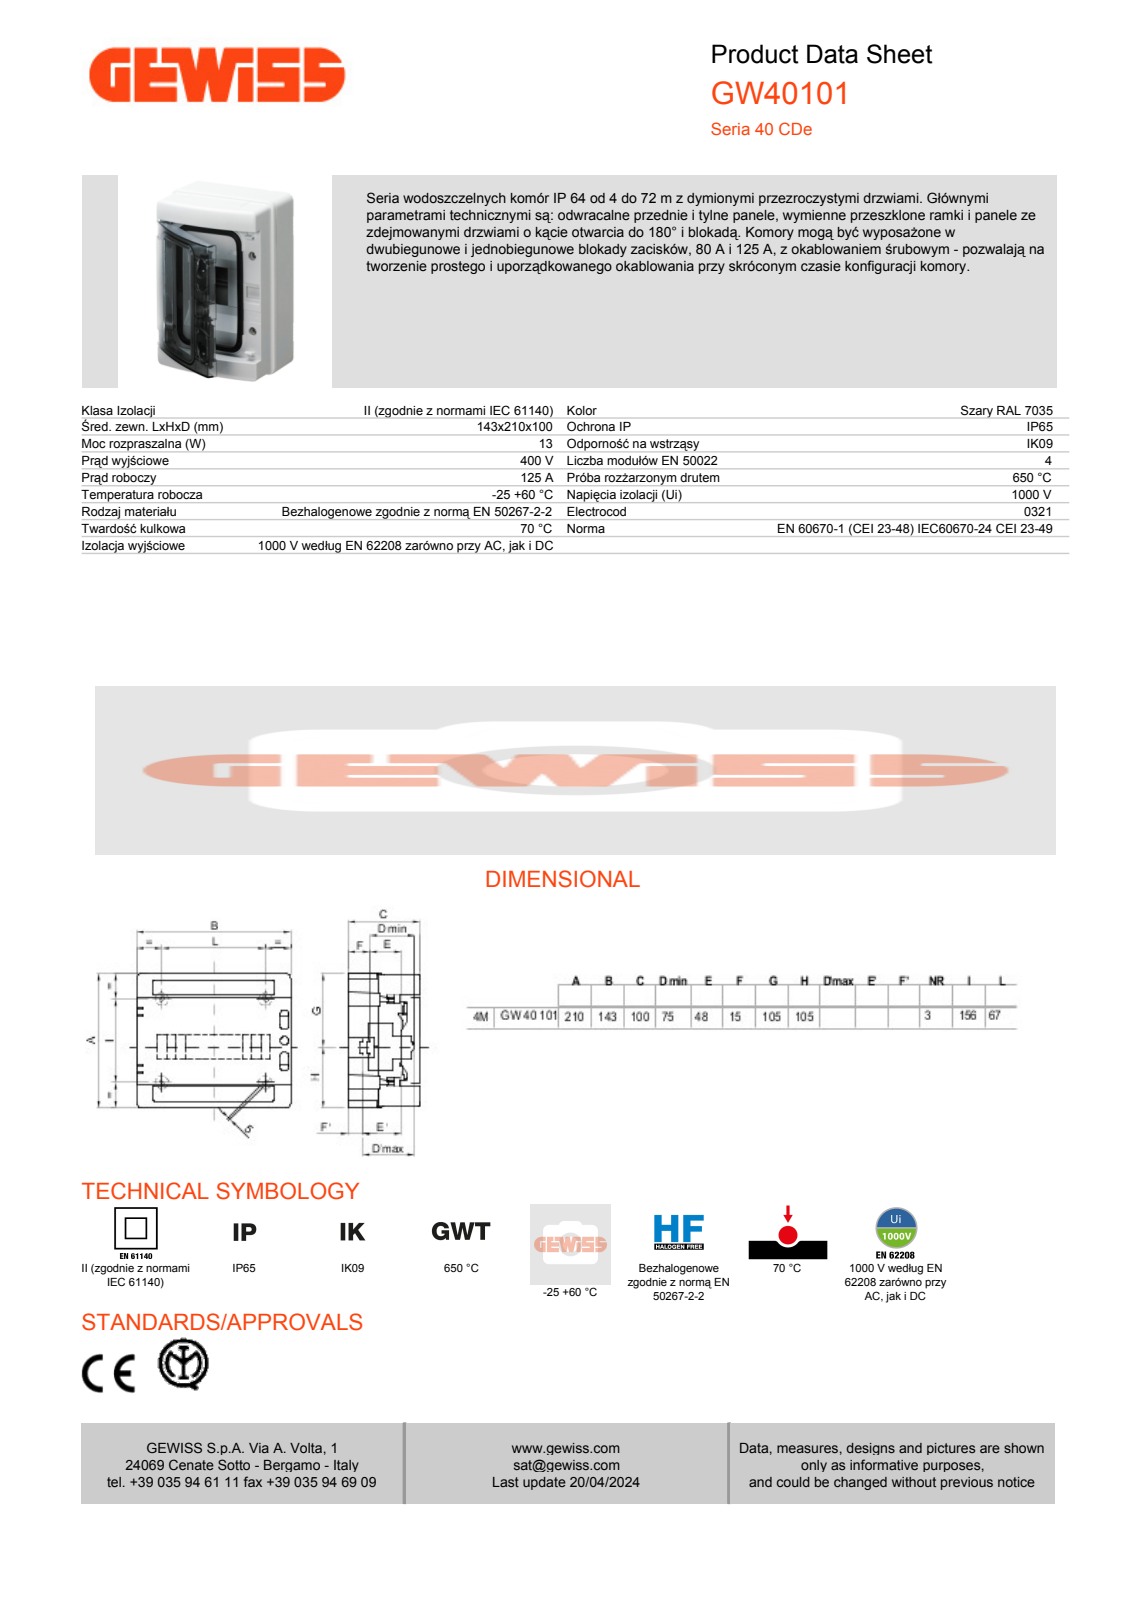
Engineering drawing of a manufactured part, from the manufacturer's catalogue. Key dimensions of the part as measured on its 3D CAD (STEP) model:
Part name (STEP PRODUCT): GW40101_SCATOLA_OR; GW40101_COPERCHIO_OR; GUIDA_DIN_X; GW40101_ASM
STEP written by: CREO PARAMETRIC BY PTC INC, 2020354 (CONFIG_CONTROL_DESIGN)
Units: millimetres
Bodies: 3 solids, 754 faces (507 planar, 134 cylindrical, 113 other)
Overall size (bounding box): 210 × 142 × 102.36
Volume: 871 162 mm³ · Surface area: 294 244 mm²
Round holes (diameter × count): ⌀3.2 ×4, ⌀4.2 ×3
Round bosses / shafts (diameter × count): ⌀21.4 ×1
Partial cylindrical surfaces — rounded edges, fillets, slot ends (radius × count): R10 ×16, R5 ×10, R3.5 ×8, R7 ×8, R0.8 ×4, R1.6 ×4, R1.8 ×4, R2 ×4
Main face-to-face distances: 3, 2.5, 204, 139, 132.67, 6, 3.5, 207, 201, 206.5
Hole centre spacings: 8.8, 48.31, 95.41, 95, 17.6, 47.5, 96.62
